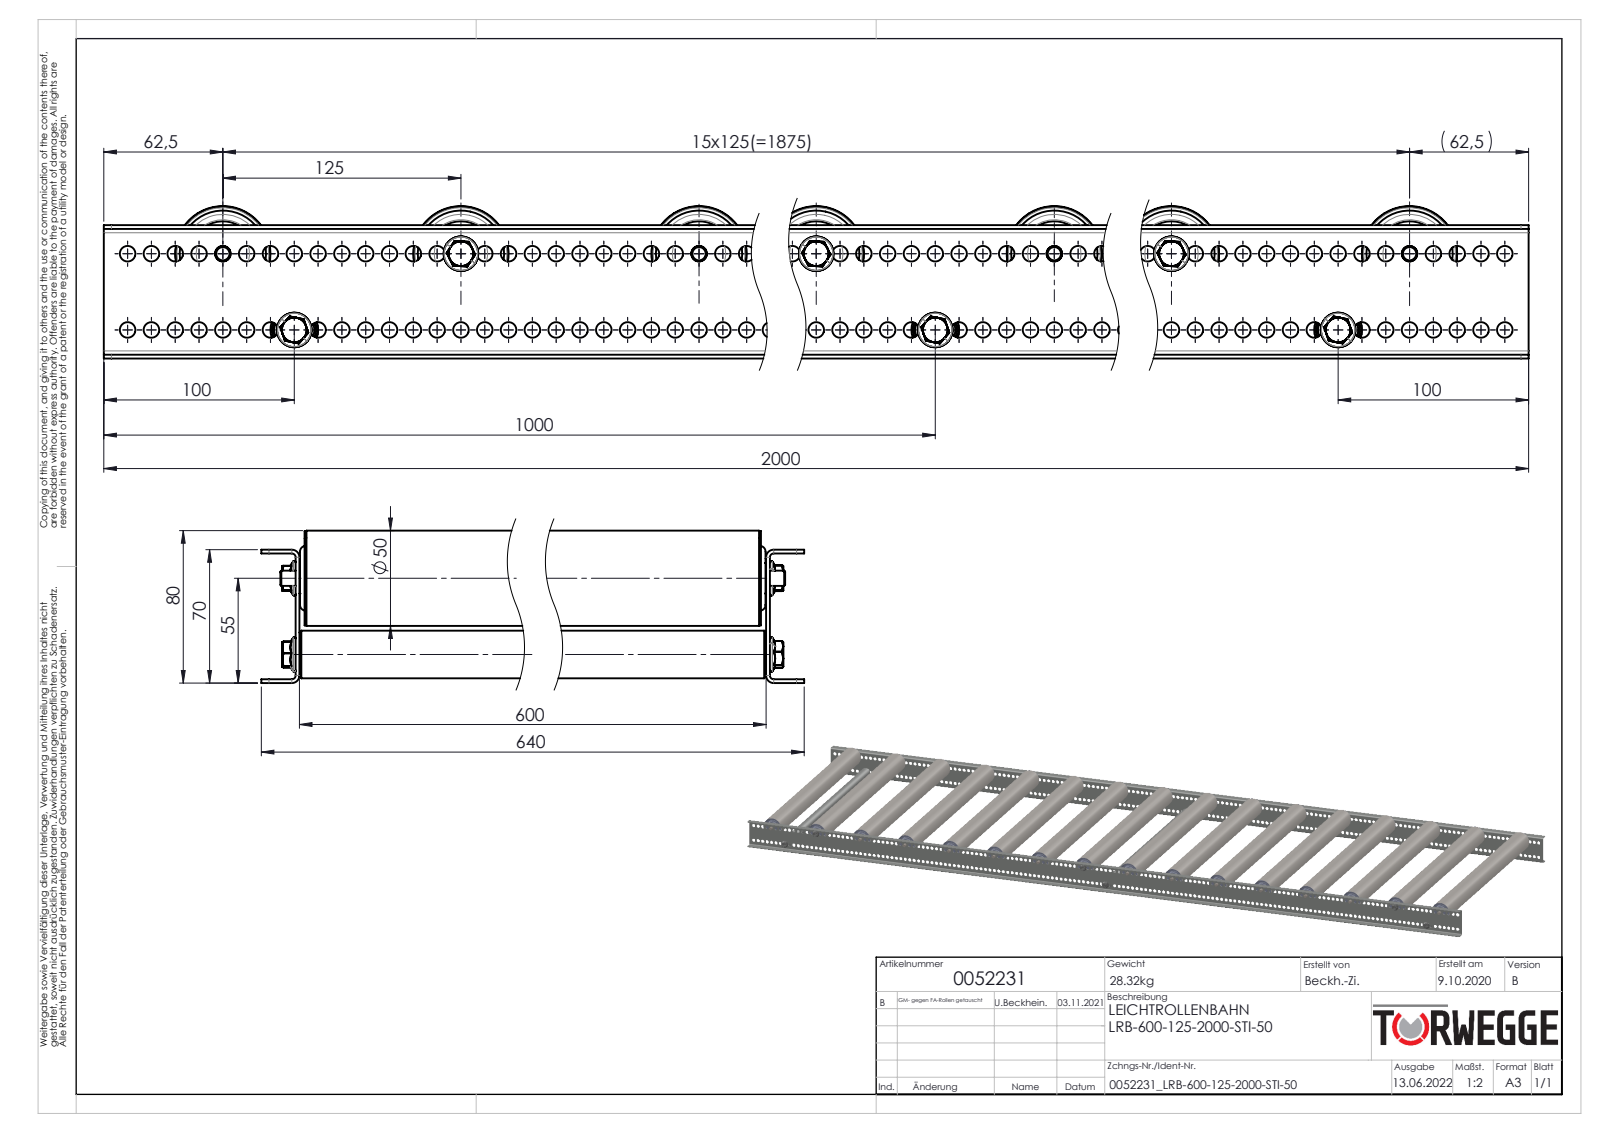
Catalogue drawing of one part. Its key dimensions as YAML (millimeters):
part_name: "0052231; 0024178_Passscheibe_DIN988_12x18x1; 0026293_Typ-TRG-50x1,5-12; Tragrollenachse-Ø8_KFG_L=620 (+8 more)"
step_written_by: "SolidWorks 2020 (AUTOMOTIVE_DESIGN)"
units: millimeters
bodies: {solids: 392, faces: 7558, planar: 1452, cylindrical: 2944, other: 3162}
overall_size: [2000, 640, 80]
volume: 4127000
surface_area: 4723000
round_holes:
  - {diameter: 8.2, count: 318}
  - {diameter: 17.1, count: 16}
  - {diameter: 18.5, count: 16}
  - {diameter: 27.7, count: 16}
  - {diameter: 45.3, count: 16}
  - {diameter: 47, count: 16}
  - {diameter: 7.6, count: 13}
  - {diameter: 6.8, count: 6}
  - {diameter: 12, count: 3}
  - {diameter: 12.2, count: 3}
  - {diameter: 19.2, count: 3}
  - {diameter: 21, count: 3}
round_bosses_or_shafts:
  - {diameter: 8, count: 19}
  - {diameter: 50, count: 16}
  - {diameter: 49.5, count: 16}
  - {diameter: 47.3, count: 16}
  - {diameter: 29.7, count: 16}
  - {diameter: 27.4, count: 16}
  - {diameter: 27.3, count: 16}
  - {diameter: 16, count: 16}
partial_cylinders:
  - {radius: 0.6, count: 26}
  - {radius: 0.75, count: 26}
  - {radius: 2.45, count: 26}
  - {radius: 4.87, count: 13}
  - {radius: 7, count: 13}
  - {radius: 2.5, count: 12}
  - {radius: 4, count: 8}
  - {radius: 2, count: 4}
face_to_face_distances: [2, 602, 68, 600, 604, 70, 66, 1, 20, 18]
hole_center_spacings: [12.5, 25, 37.5, 50, 62.5, 75, 87.5, 100]
